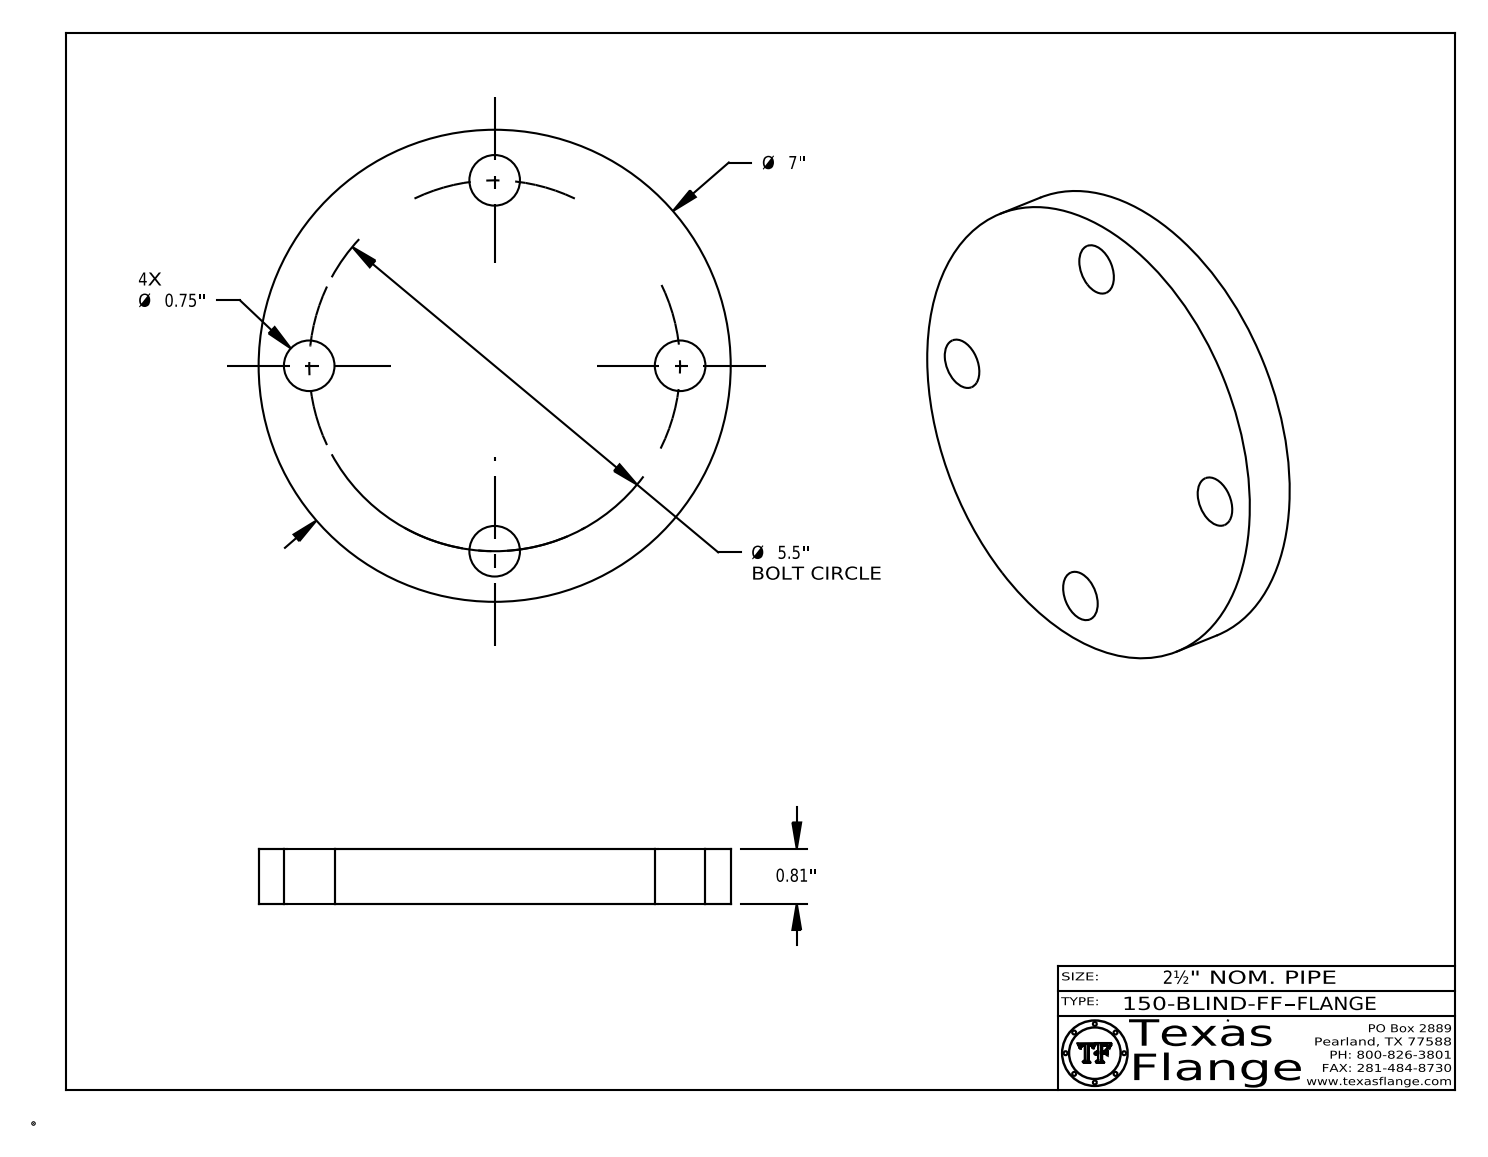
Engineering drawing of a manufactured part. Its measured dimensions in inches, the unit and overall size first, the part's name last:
Units: inches
Overall size (bounding box): 7 × 7 × 0.81
Round holes (diameter × count): ⌀0.75 ×4, ⌀0.495 ×1
Round bosses / shafts (diameter × count): ⌀0.03 ×8, ⌀7 ×1, ⌀0.39 ×1
Main face-to-face distances: 0.81, 0.795, 0.015, 0.148, 0.144, 0.027, 0.122, 0.096, 0.021, 0.101
Hole centre spacings: 3.889, 2.105, 5.081, 5.5
Volume: 29.74 in³ · Surface area: 98.97 in²
Bodies: 1 solid, 397 faces (367 planar, 30 cylindrical, 0 other)
Part name (STEP PRODUCT): 150-BLIND-FF
STEP written by: CATIA V5 STEP AP214 (AUTOMOTIVE_DESIGN)
